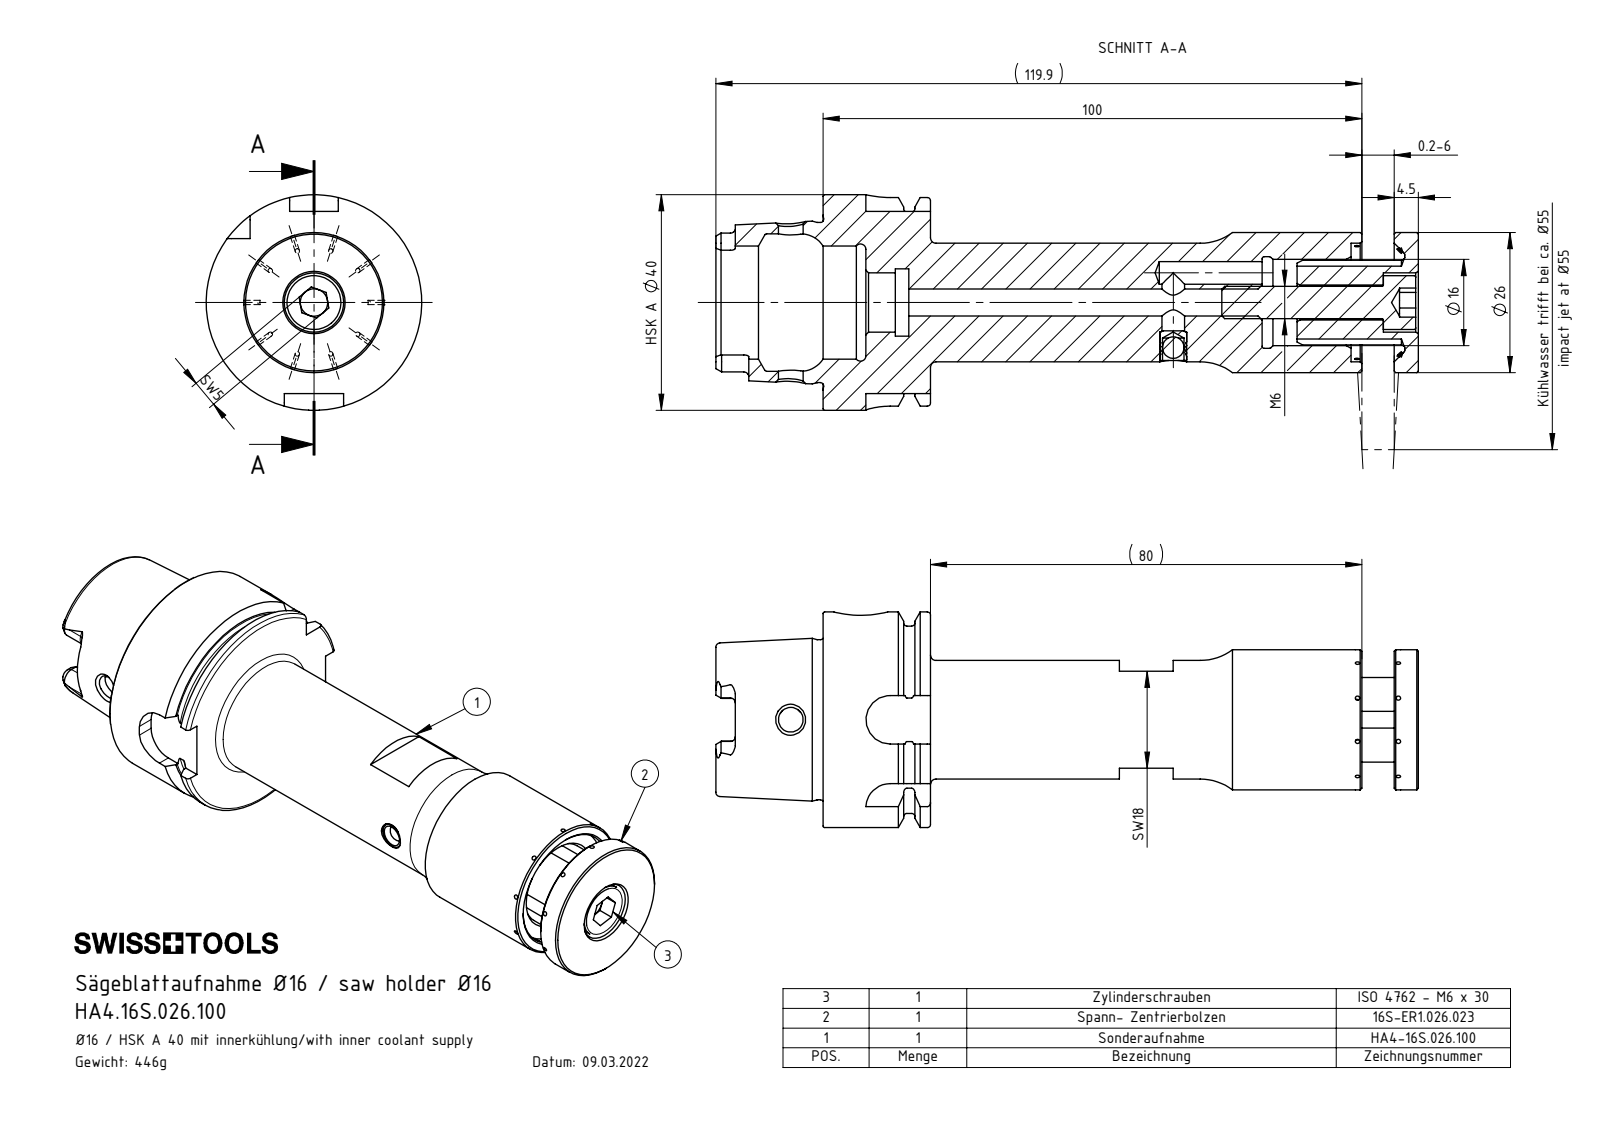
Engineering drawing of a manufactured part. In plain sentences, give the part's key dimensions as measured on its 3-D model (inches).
The part is named "HA4.16S.026.100; ISO 4762 - M6 x 30; HA4-16S.026.100_A_Fertigbearbeitung; KVT_MB_600_050 (+1 more)". Its 3-D file was written by "SolidWorks 2017 (AUTOMOTIVE_DESIGN)". It is 5 solids with 345 faces: 74 planar, 132 cylindrical and 139 other. Overall it measures 5.134 by 1.575 by 1.575 inches. Its volume is 3.536 cubic inches and its surface area 34.33 square inches. Round holes: 20 of diameter 0.031, 2 of diameter 0.165, 1 of diameter 0.157, 1 of diameter 0.181, 1 of diameter 0.197, 1 of diameter 0.256, 1 of diameter 0.394, 1 of diameter 0.433, 1 of diameter 0.492, 1 of diameter 0.669, 1 of diameter 0.827, 1 of diameter 0.866. Round bosses or shafts: 1 of diameter 1.575, 1 of diameter 1.368, 1 of diameter 1.17, 1 of diameter 1.024, 1 of diameter 0.63, 1 of diameter 0.394, 1 of diameter 0.236, 1 of diameter 0.197. Partial cylindrical surfaces (rounded edges, fillets, slot ends): 6 of radius 0.035, 4 of radius 0.065, 4 of radius 0.074, 4 of radius 0.177. The main face-to-face distances are 3.565, 0.785, 4.35, 0.472, 0.313, 0.236, 0.709, 0.256, 0.886, 3.152. The hole center spacings are 0.356, 0.356, 0.217, 2.795.
